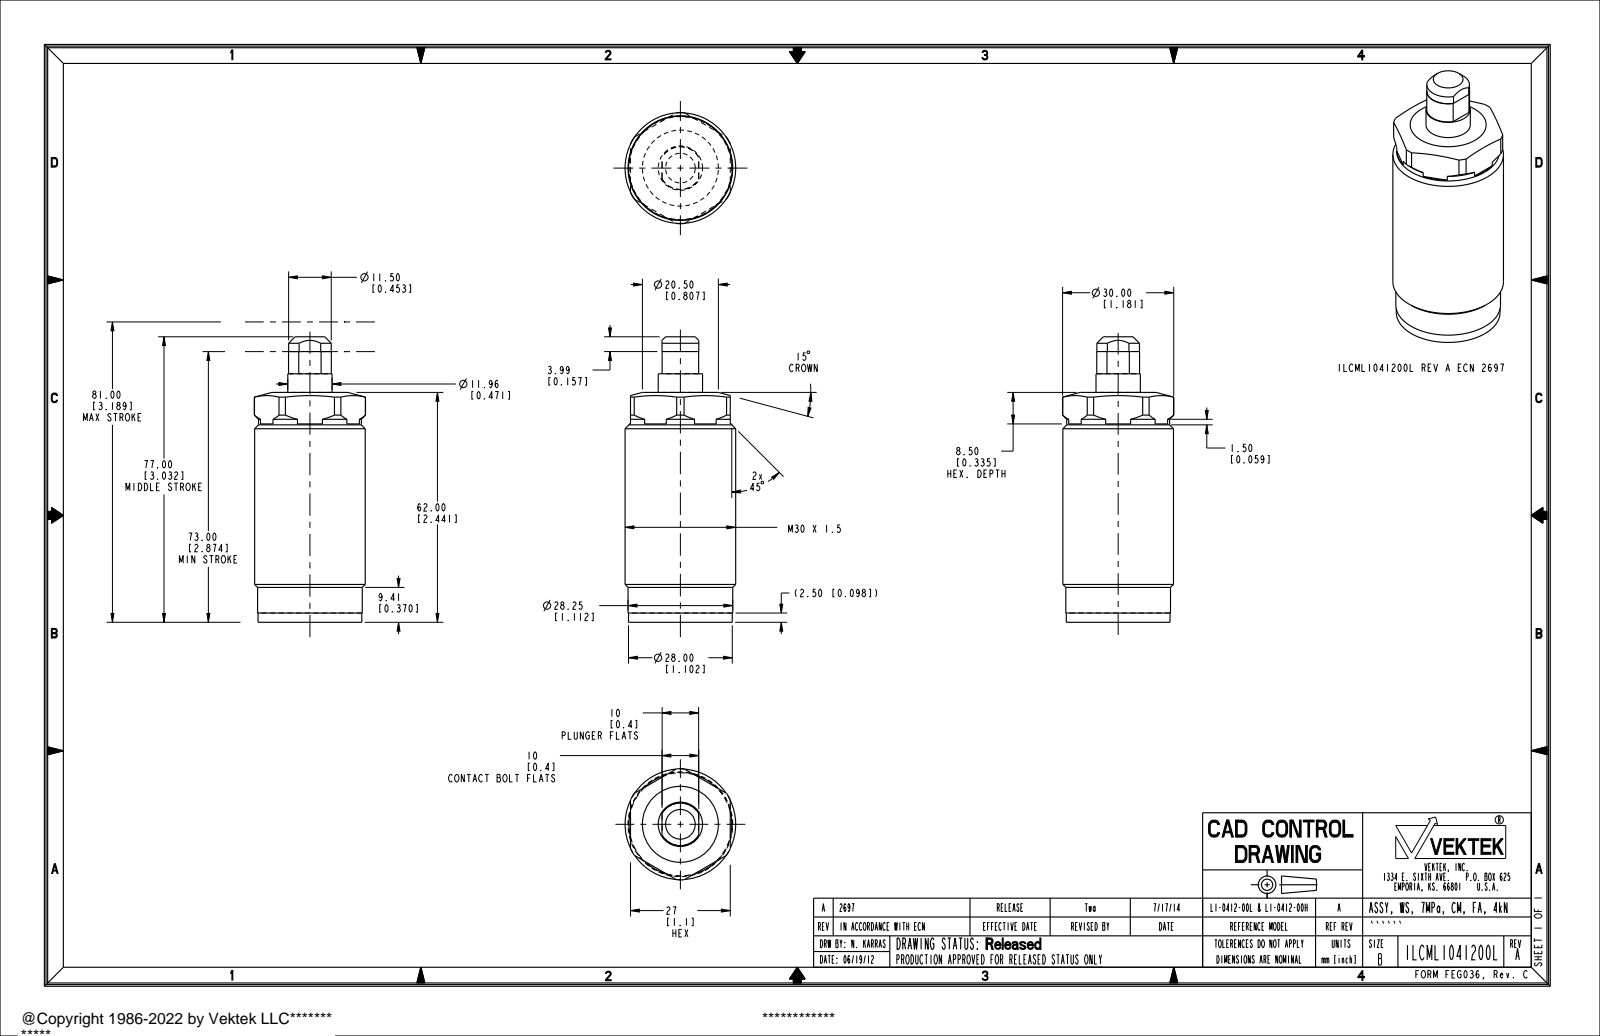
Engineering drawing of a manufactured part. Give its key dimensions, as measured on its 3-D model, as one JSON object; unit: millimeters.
{"part_name": "ILCML1041200L", "step_written_by": "PRO/ENGINEER BY PARAMETRIC TECHNOLOGY CORPORATION, 2013320 (AUTOMOTIVE_DESIGN)", "units": "millimeters", "bodies": {"solids": 1, "faces": 59, "planar": 25, "cylindrical": 20, "other": 14}, "overall_size": [77, 30, 29.85], "volume_mm3": 43212, "surface_area_mm2": 7498, "round_bosses_or_shafts": [[29.85, 1], [28.25, 1], [28, 1], [27.75, 1], [11.96, 1]], "partial_cylinders_radius": [[5.75, 1], [5.78, 1], [15, 1]], "face_to_face_distances": [26.92, 62, 8.54, 18.38, 77, 15, 8.5, 9.84, 18.42, 9.88]}
